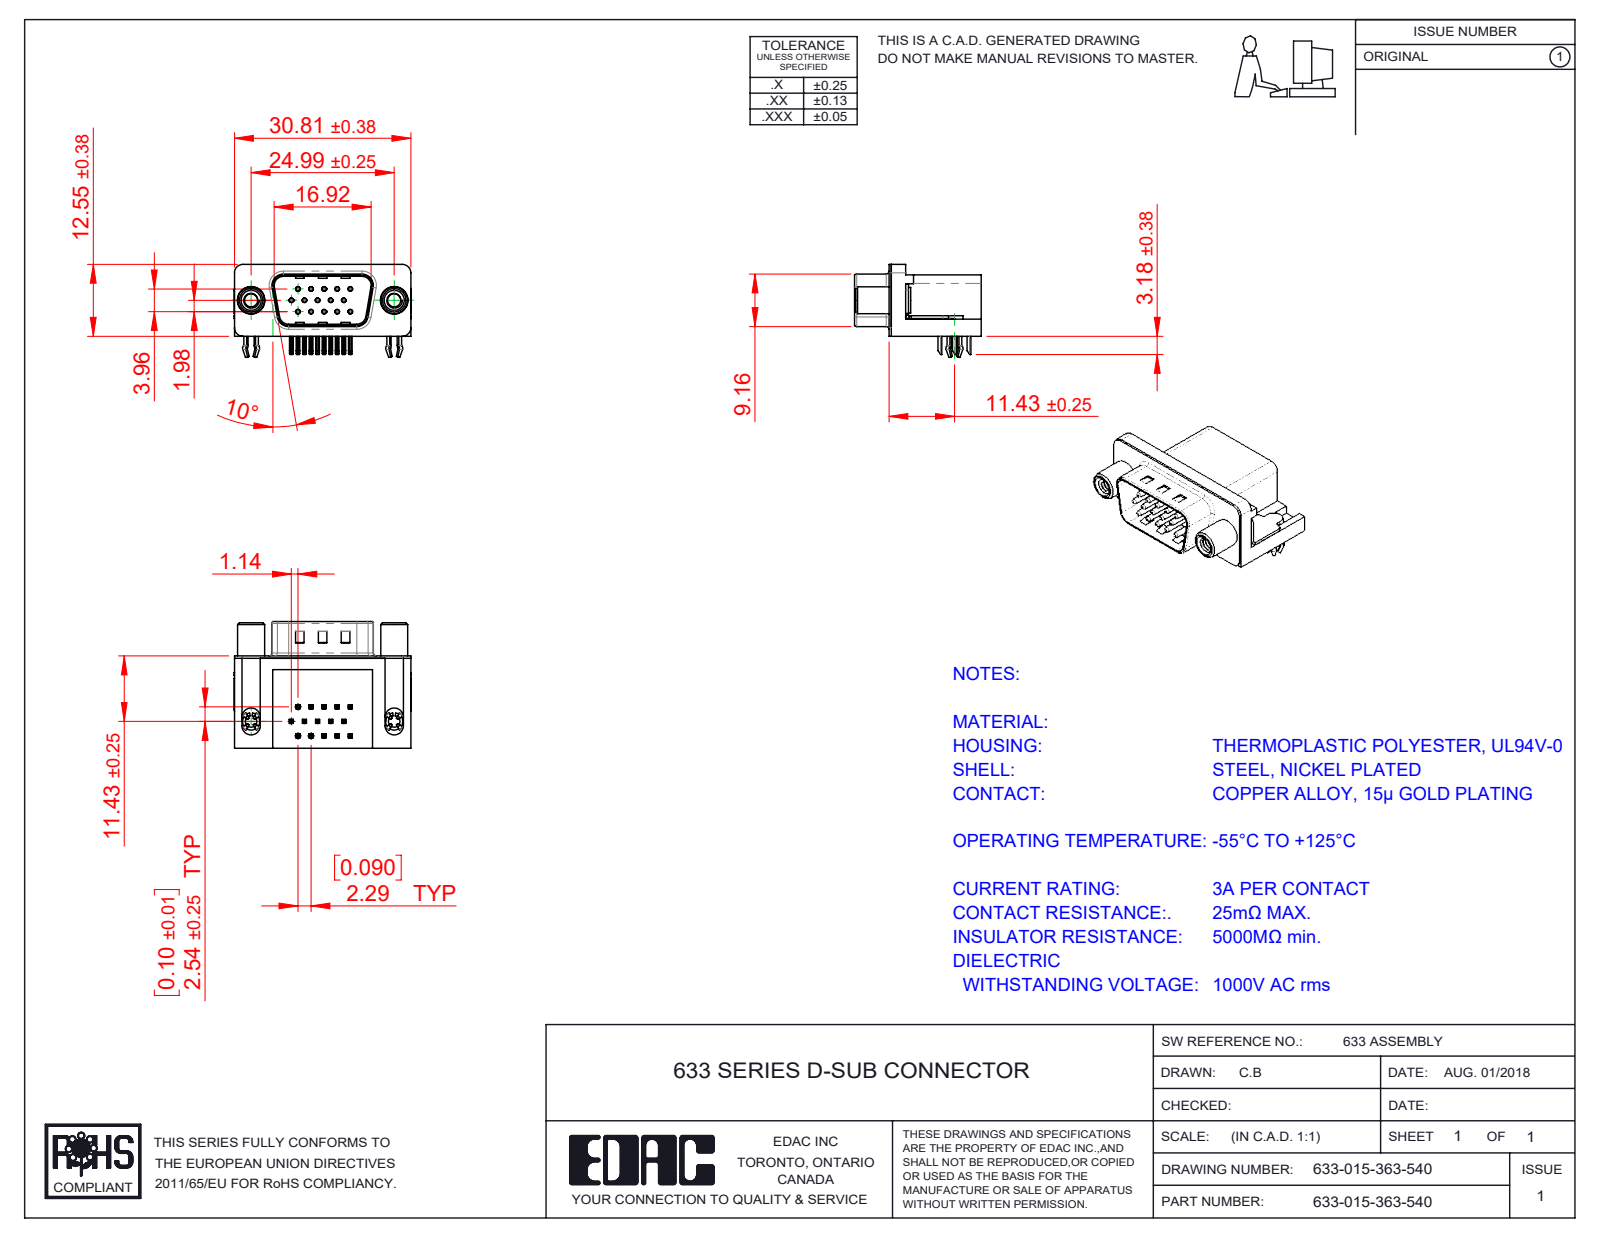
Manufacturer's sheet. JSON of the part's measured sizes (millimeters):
{"part_name": "633 Housing_15 Contact; 633 4 Prong Board Lock; 633 Contact Bottom; 633 Contact Top (+4 more)", "step_written_by": "SolidWorks 2016 (CONFIG_CONTROL_DESIGN)", "units": "millimeters", "bodies": {"solids": 21, "faces": 1557, "planar": 895, "cylindrical": 457, "other": 205}, "overall_size": [30.89, 22.1, 16.25], "volume_mm3": 4173, "surface_area_mm2": 5698, "round_holes": [[0.35, 15], [0.8, 15], [2, 2], [2.3, 2], [3.1, 2], [4, 2], [4.8, 2], [5, 2]], "round_bosses_or_shafts": [[0.75, 15], [4.9, 2], [4.7, 2], [4.5, 2], [3.85, 2], [3, 2]], "partial_cylinders_radius": [[0.25, 64], [0.12, 30], [1, 16], [0.5, 9], [1.6, 8], [1.5, 7], [0.9, 4], [2, 4]], "face_to_face_distances": [0.4, 10.35, 15.7, 2.9, 6.7, 2.5, 16.1, 0.35, 10.7, 13.2], "hole_center_spacings": [3.96, 2.28, 4.57, 2.29, 6.05, 6.86, 7.92, 6.04]}
